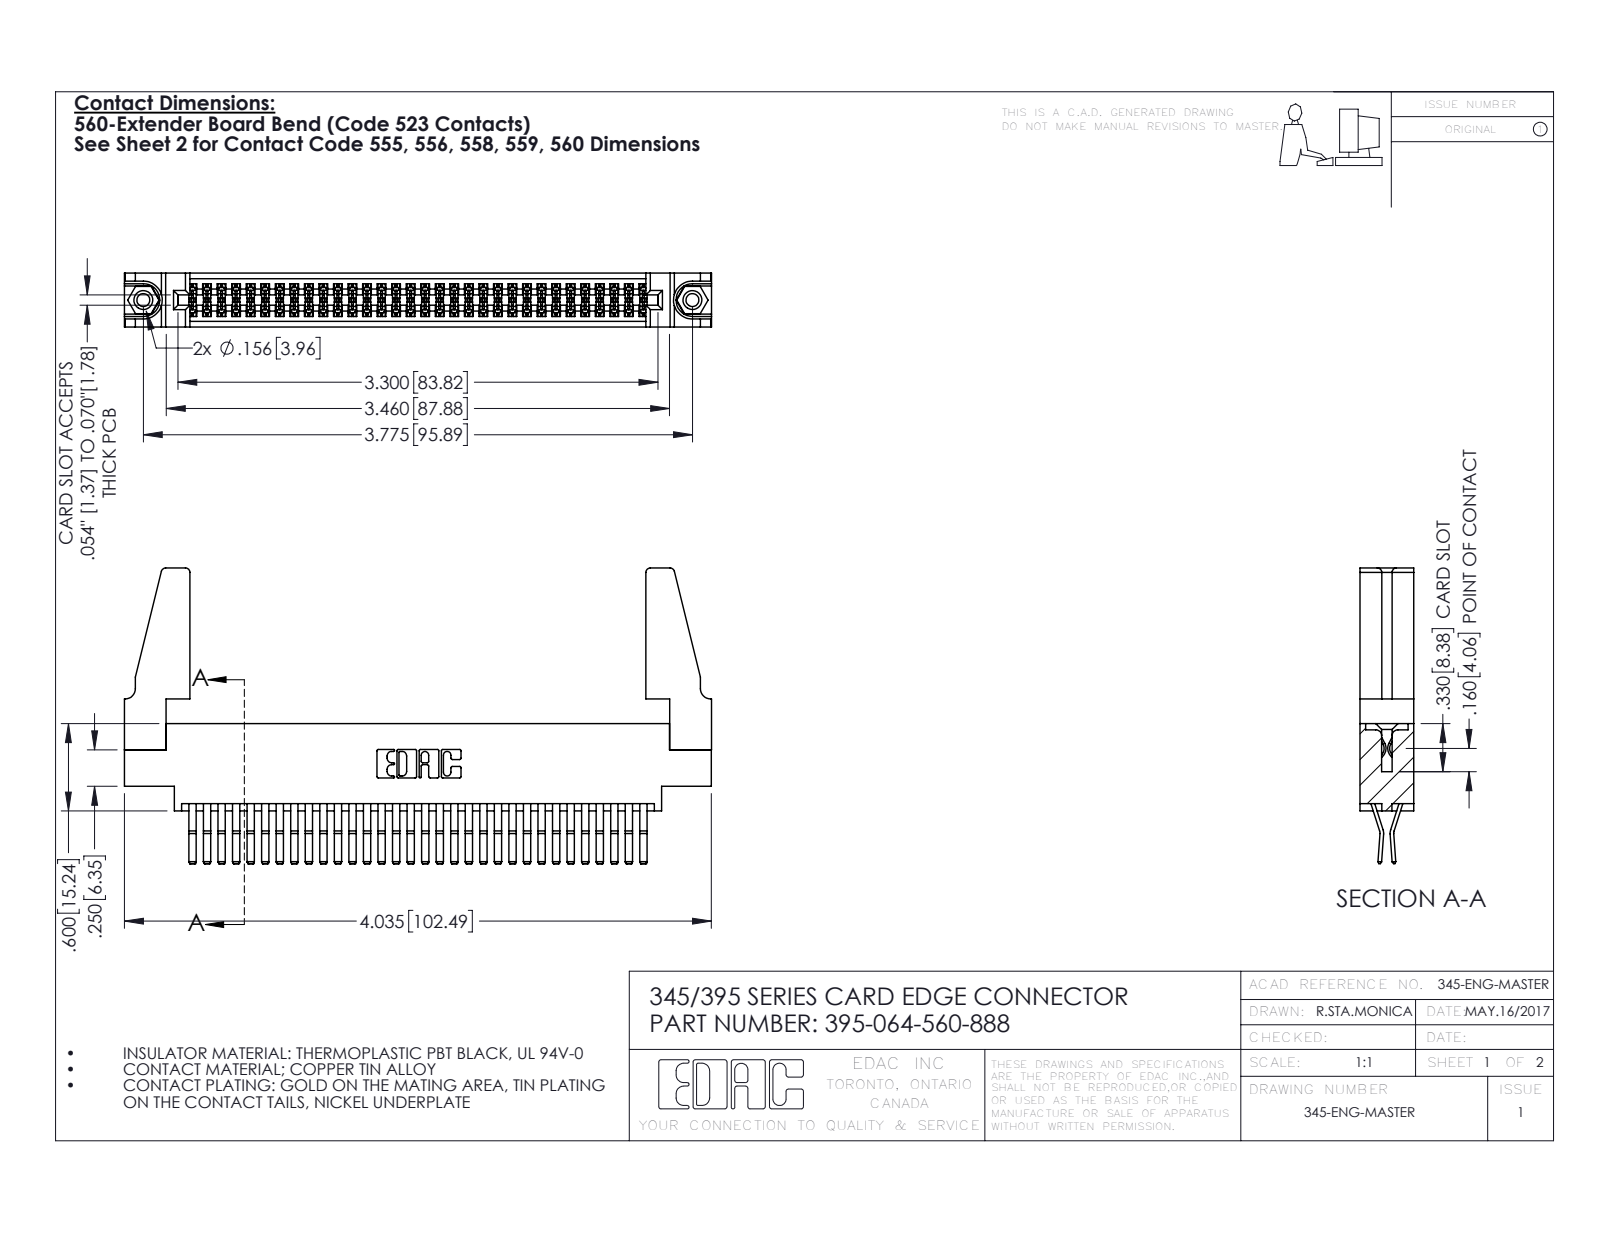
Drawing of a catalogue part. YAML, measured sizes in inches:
part_name: "345-250-001_345-250-001-102; 345-292-001_560 Tail; 395-064-560-888; 345 Part_0.170 Offset - 0.156 Dia-TH (+1 more)"
step_written_by: "SolidWorks 2016 (CONFIG_CONTROL_DESIGN)"
units: inches
bodies: {solids: 69, faces: 3582, planar: 2268, cylindrical: 1298, other: 16}
overall_size: [4.036, 2.032, 0.37]
volume: 0.819
surface_area: 29.74
round_holes:
  - {diameter: 0.089, count: 2}
  - {diameter: 0.125, count: 2}
  - {diameter: 0.156, count: 2}
  - {diameter: 0.064, count: 1}
round_bosses_or_shafts:
  - {diameter: 0.155, count: 2}
partial_cylinders:
  - {radius: 0.006, count: 97}
  - {radius: 0.01, count: 22}
  - {radius: 0.03, count: 8}
  - {radius: 0.007, count: 6}
  - {radius: 0.031, count: 6}
  - {radius: 0.026, count: 3}
  - {radius: 0.01, count: 2}
  - {radius: 0.014, count: 2}
face_to_face_distances: [0.072, 0.37, 0.298, 0.025, 0.2, 0.098, 0.272, 0.225, 0.175, 0.149]
hole_center_spacings: [0.27, 3.54, 3.775]
